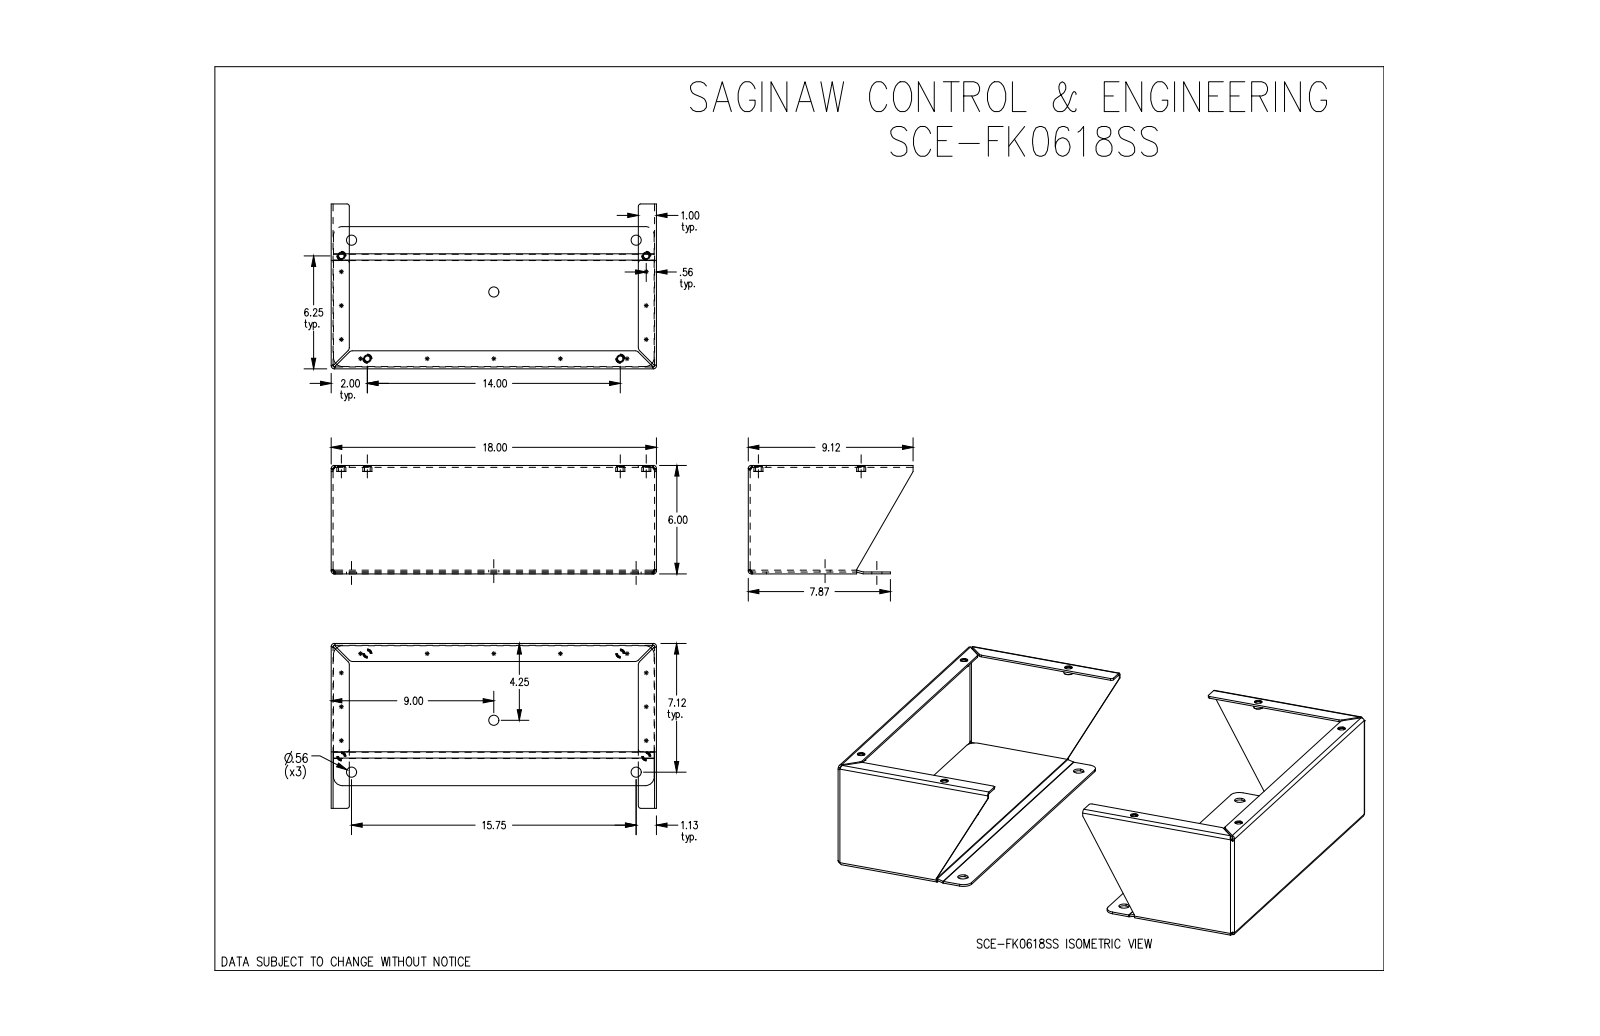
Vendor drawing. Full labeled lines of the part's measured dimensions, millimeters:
Part name (STEP PRODUCT): SCE-FK0618SS
STEP written by: SolidWorks 2019 (CONFIG_CONTROL_DESIGN)
Units: millimetres
Bodies: 12 solids, 286 faces (120 planar, 110 cylindrical, 56 other)
Overall size (bounding box): 609.6 × 457.2 × 152.4
Volume: 1 316 000 mm³ · Surface area: 1 017 000 mm²
Round holes (diameter × count): ⌀7.9 ×8, ⌀10.5 ×8, ⌀14.3 ×6
Round bosses / shafts (diameter × count): ⌀12.7 ×8, ⌀10.5 ×8
Partial cylindrical surfaces — rounded edges, fillets, slot ends (radius × count): R4.2 ×16, R1.6 ×14, R3.2 ×8, R5.6 ×8, R12.7 ×8, R1.6 ×2
Main face-to-face distances: 2.6, 607, 454.6, 147.1, 2.6, 149.7, 149.8, 609.6, 604.3, 457.2
Hole centre spacings: 26.3, 149, 168, 201, 220.2, 270.4, 378.1, 404.3
